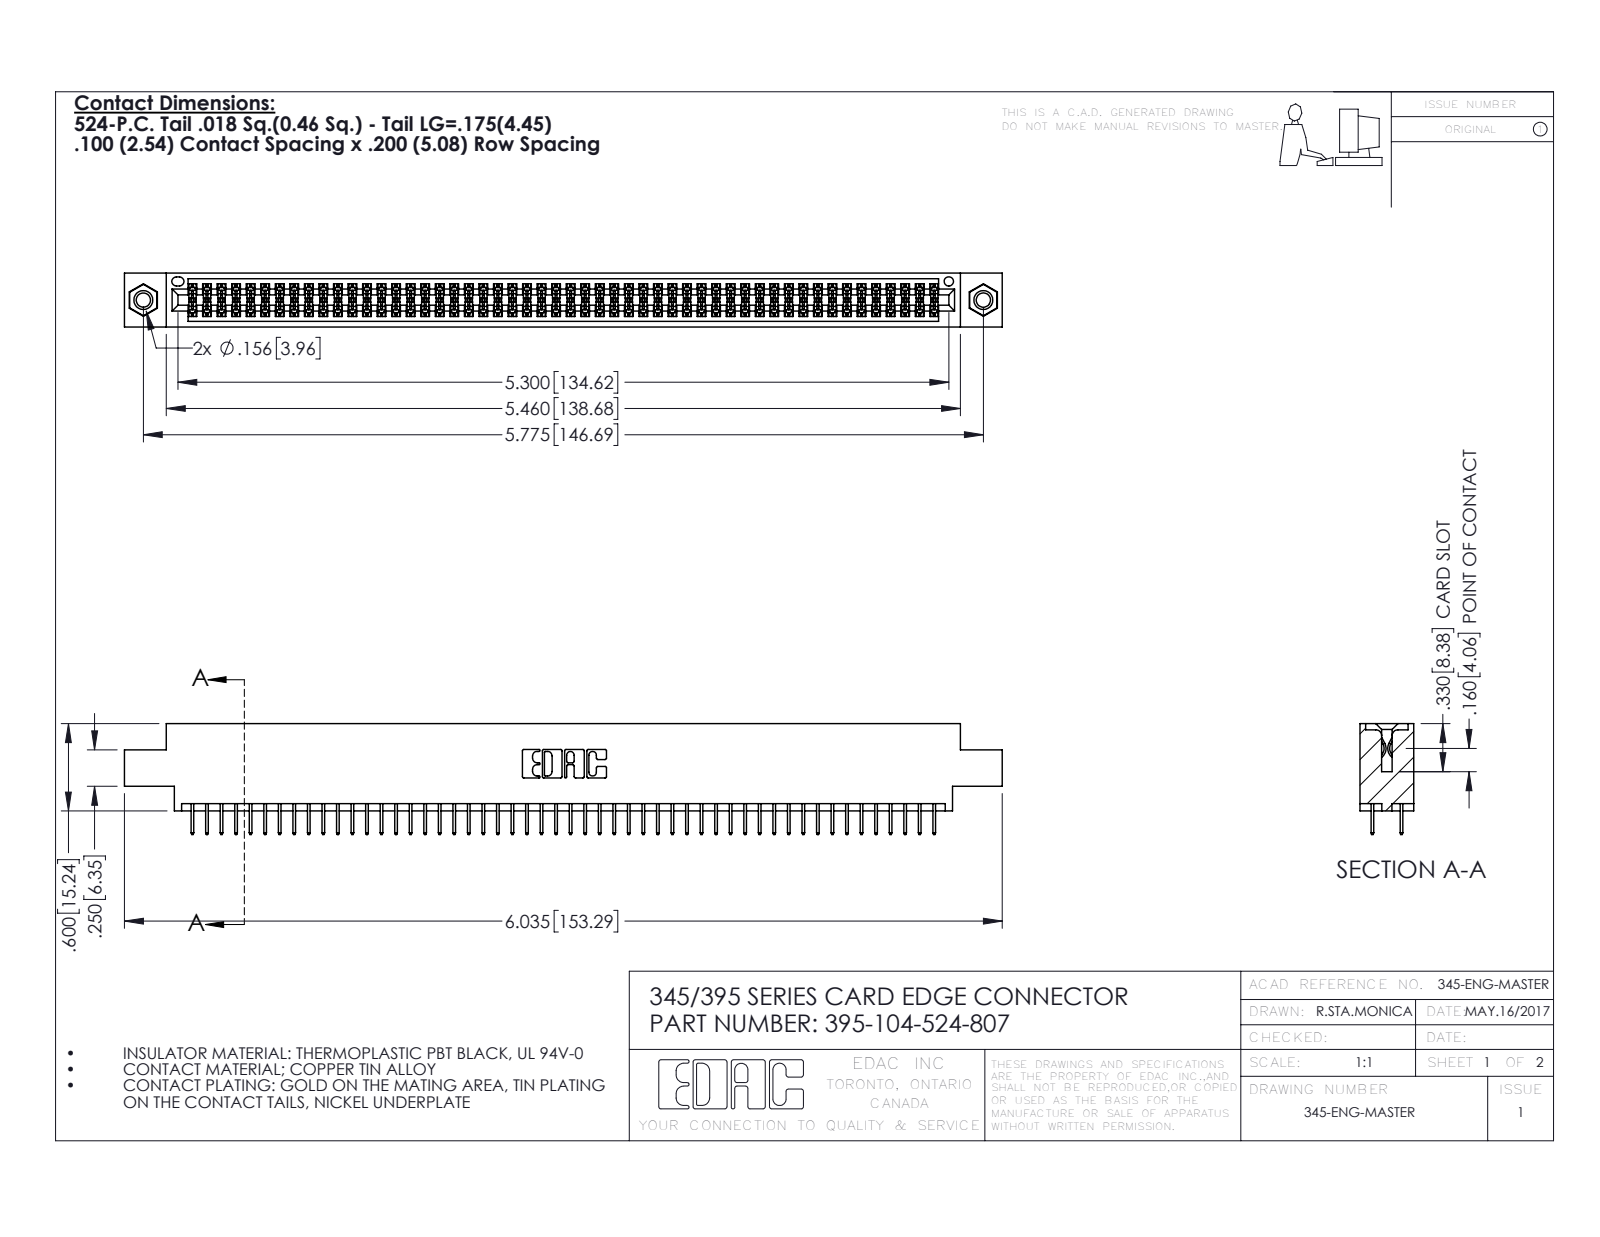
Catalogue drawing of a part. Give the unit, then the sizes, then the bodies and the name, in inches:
Units: inches
Overall size (bounding box): 6.035 × 0.762 × 0.37
Round holes (diameter × count): ⌀0.098 ×2, ⌀0.125 ×2, ⌀0.156 ×2, ⌀0.064 ×1
Round bosses / shafts (diameter × count): ⌀0.155 ×2
Partial cylindrical surfaces — rounded edges, fillets, slot ends (radius × count): R0.006 ×156, R0.01 ×22, R0.007 ×6, R0.031 ×6, R0.026 ×3, R0.014 ×2, R0.019 ×2, R0.022 ×2
Main face-to-face distances: 0.072, 0.298, 0.37, 0.2, 0.098, 0.272, 0.025, 0.225, 0.072, 0.175
Hole centre spacings: 0.27, 5.539, 5.775
Volume: 0.897 in³ · Surface area: 33.6 in²
Bodies: 107 solids, 5806 faces (4172 planar, 1618 cylindrical, 16 other)
Part name (STEP PRODUCT): 345-292-001_345-293-124; 395-104-524-807; 345 Part_0.170 Offset - 0.156 Dia-TI; 345-250-001_345-250-005-103
STEP written by: SolidWorks 2016 (CONFIG_CONTROL_DESIGN)
